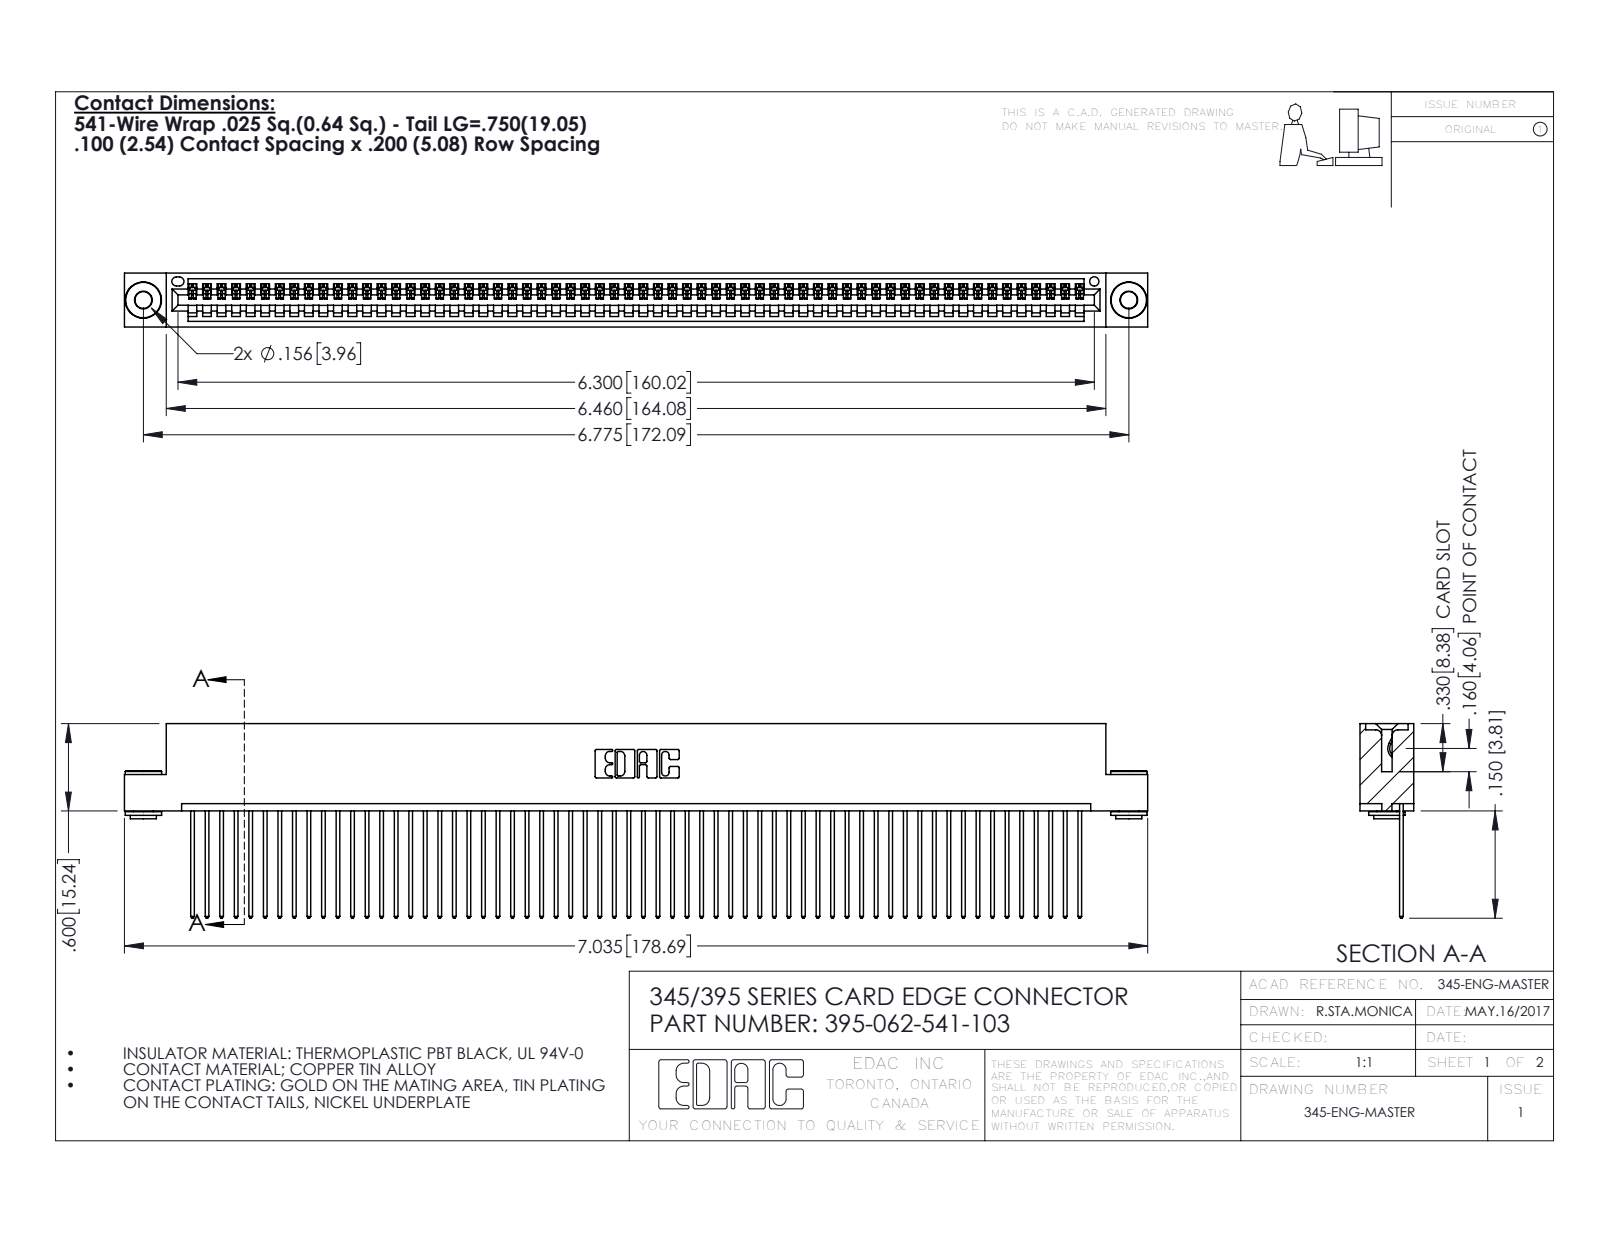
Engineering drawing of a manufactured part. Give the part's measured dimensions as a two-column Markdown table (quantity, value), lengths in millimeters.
| quantity | value |
| --- | --- |
| part name | 345 Part_Flush Mounting Lugs - 0.156 Dia-TH; 395-062-541-103; 345-292-001_345-293-141; 345-250-002_345-250-002-102 |
| STEP written by | SolidWorks 2016 (CONFIG_CONTROL_DESIGN) |
| units | millimeters |
| bodies | 65 solids, 3760 faces (2570 planar, 1182 cylindrical, 8 other) |
| overall size | 178.7 × 34 × 9.4 |
| volume | 17 350 mm³ |
| surface area | 24 760 mm² |
| round holes (diameter × count) | 2.9 × 2, 4 × 2, 1.6 × 1 |
| round bosses / shafts (diameter × count) | 6.4 × 2, 4.6 × 2, 3.5 × 2 |
| partial cylindrical surfaces (radius × count) | 0.2 × 124, 0.3 × 124, 0.3 × 22, 0.2 × 6, 0.8 × 6, 0.7 × 3, 0.8 × 2, 1 × 2 |
| main face-to-face distances | 1.8, 7.6, 0.6, 2.5, 6.9, 9.4, 5.1, 5.7, 3.8, 1.8 |
| hole center spacings | 6.9, 166.1, 172.1 |
